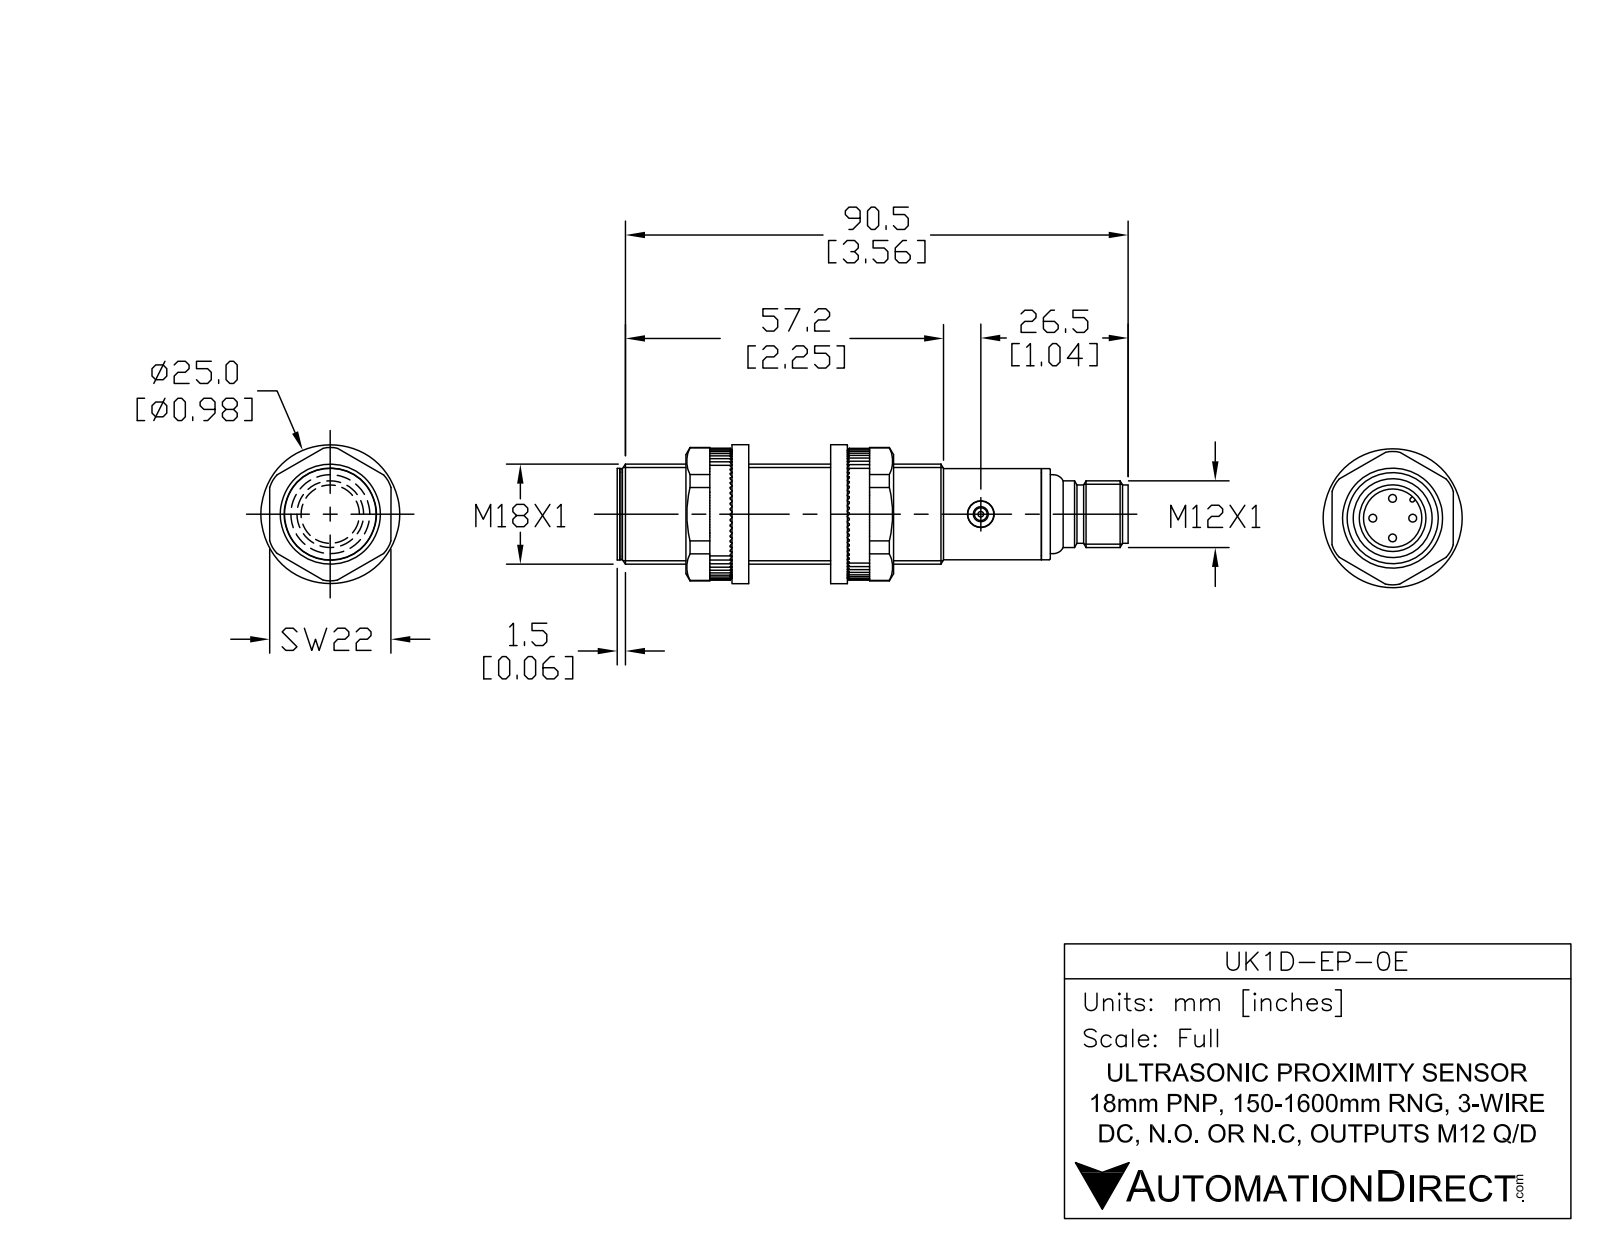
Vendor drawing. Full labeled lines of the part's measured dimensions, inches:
Part name (STEP PRODUCT): UK1D-EP-0E
STEP written by: SolidWorks 2017 (AUTOMOTIVE_DESIGN)
Units: inches
Bodies: 6 solids, 106 faces (21 planar, 48 cylindrical, 37 other)
Overall size (bounding box): 3.606 × 0.709 × 0.709
Volume: 1.202 in³ · Surface area: 10.68 in²
Round holes (diameter × count): ⌀0.106 ×1, ⌀0.185 ×1, ⌀0.276 ×1, ⌀0.327 ×1, ⌀0.374 ×1
Round bosses / shafts (diameter × count): ⌀0.039 ×4, ⌀0.709 ×1, ⌀0.654 ×1, ⌀0.646 ×1, ⌀0.622 ×1, ⌀0.559 ×1, ⌀0.472 ×1, ⌀0.413 ×1
Partial cylindrical surfaces — rounded edges, fillets, slot ends (radius × count): R0.024 ×1
Main face-to-face distances: 2.957, 0.039, 2.996, 0.037, 2.994, 0.043, 0.157, 3.055, 3.053, 3.016
